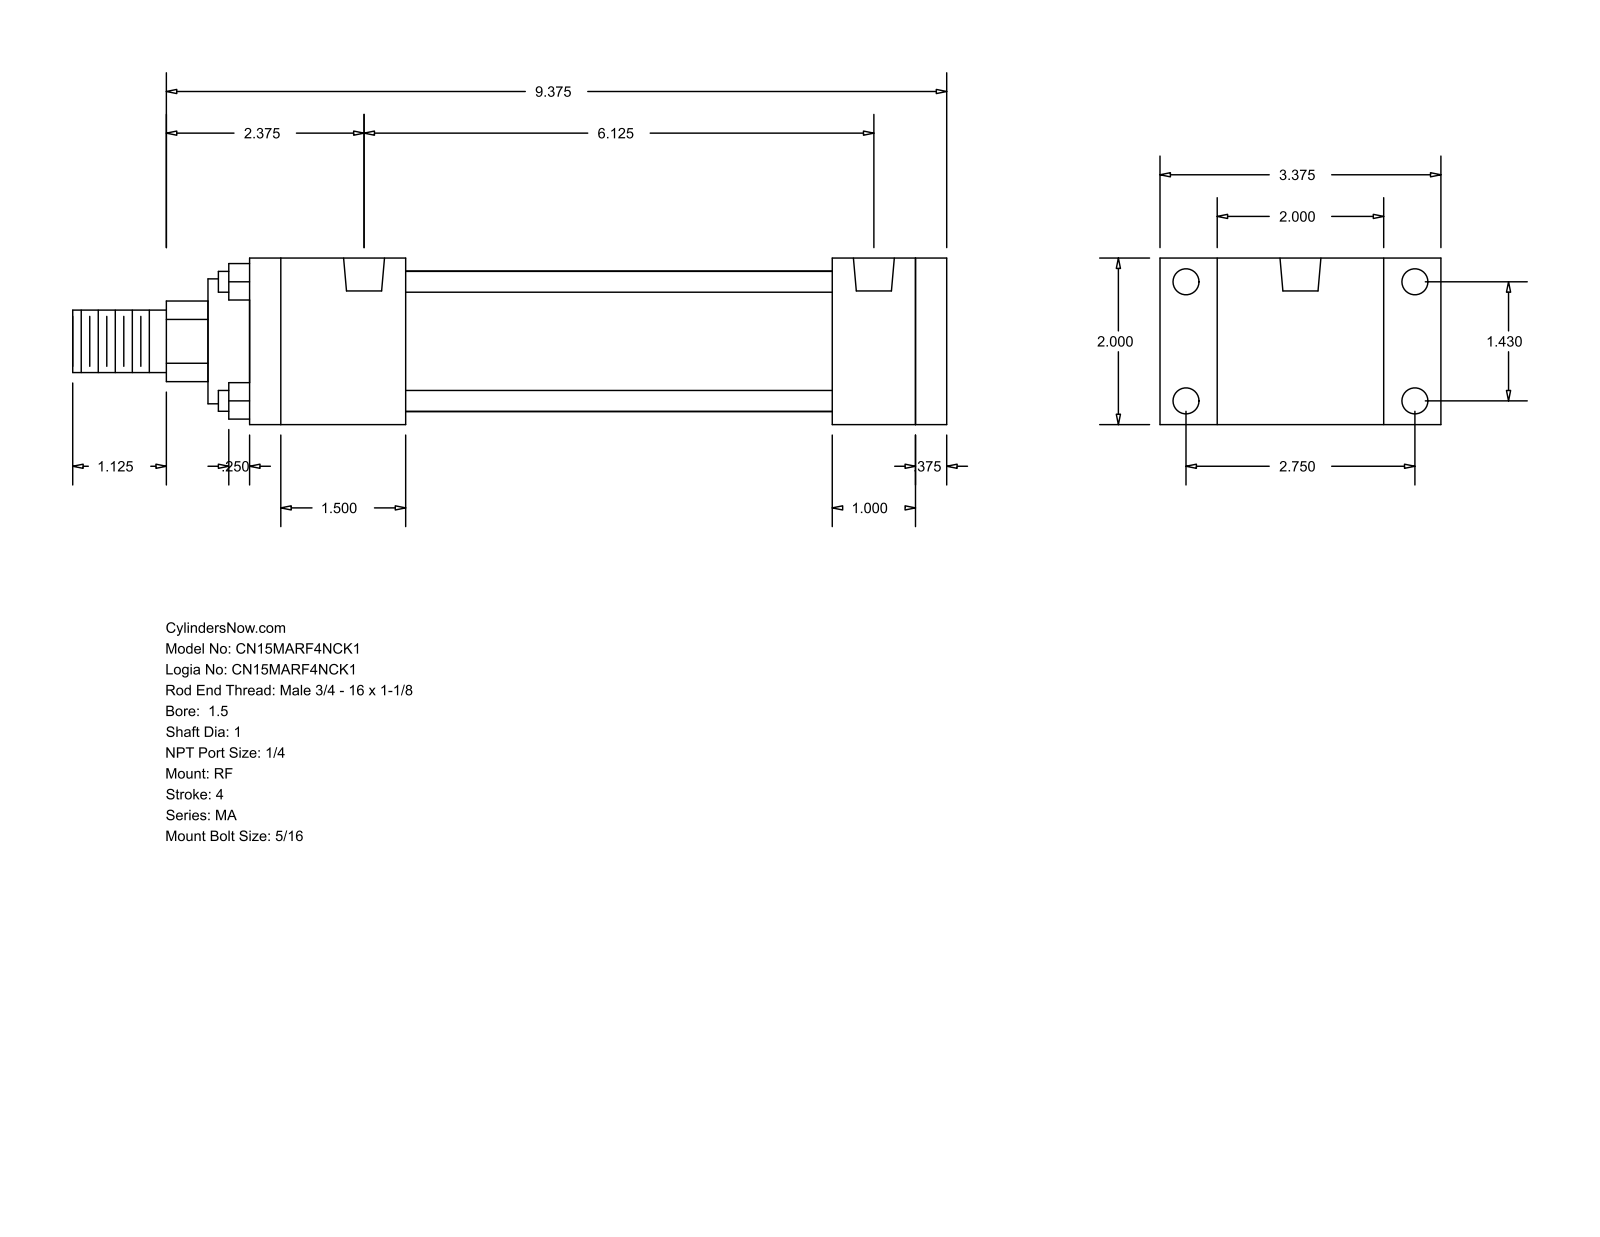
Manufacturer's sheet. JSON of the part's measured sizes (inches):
{"part_name": "MA_RF__0150_1", "step_written_by": "GSSL Pune (CONFIG_CONTROL_DESIGN)", "units": "inches", "bodies": {"solids": 0, "faces": 92, "planar": 64, "cylindrical": 28, "other": 0}, "overall_size": [10.5, 3.375, 2], "round_holes": [[0.313, 8], [0.492, 2]], "round_bosses_or_shafts": [[0.25, 4], [1.69, 1], [1.5, 1], [1, 1], [0.75, 1]], "partial_cylinders_radius": [[0.484, 1]], "face_to_face_distances": [2, 0.375, 8.375, 8, 1, 7, 1.375, 1.875, 5.125, 6.125], "hole_center_spacings": [1.43, 2.75, 3.099, 6.125]}
